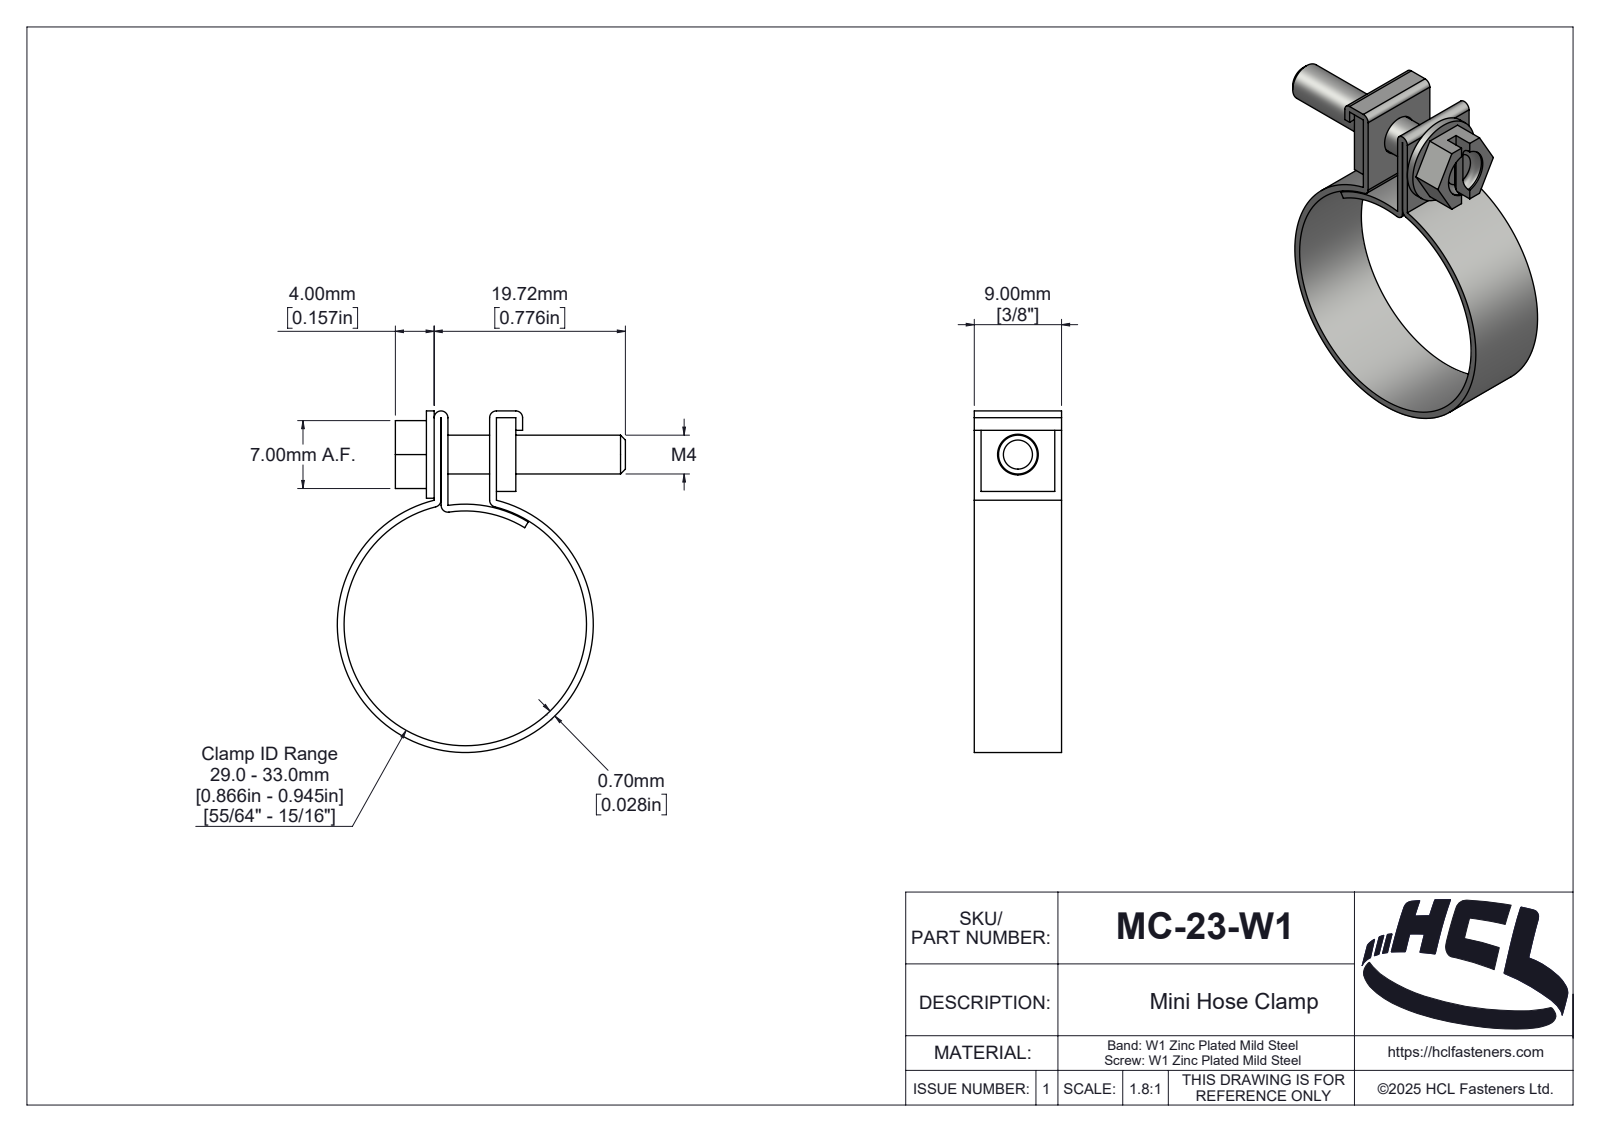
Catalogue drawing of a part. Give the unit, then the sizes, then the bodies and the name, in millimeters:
Units: millimetres
Overall size (bounding box): 35.21 × 29.71 × 9
Round holes (diameter × count): ⌀4.2 ×1, ⌀5 ×1, ⌀25 ×1
Round bosses / shafts (diameter × count): ⌀26.4 ×1, ⌀9 ×1, ⌀4 ×1
Partial cylindrical surfaces — rounded edges, fillets, slot ends (radius × count): R0.7 ×5, R0.2 ×1, R0.71 ×1, R0.81 ×1, R1.01 ×1, R1.06 ×1, R1.28 ×1, R1.81 ×1
Main face-to-face distances: 0.7, 5, 0.72, 5.72, 6.42, 7, 9, 2, 2.7, 8.42
Volume: 1 193 mm³ · Surface area: 2 878 mm²
Bodies: 3 solids, 170 faces (38 planar, 79 cylindrical, 53 other)
Part name (STEP PRODUCT): MC-23-W1
STEP written by: SolidWorks 2025 (AUTOMOTIVE_DESIGN)
